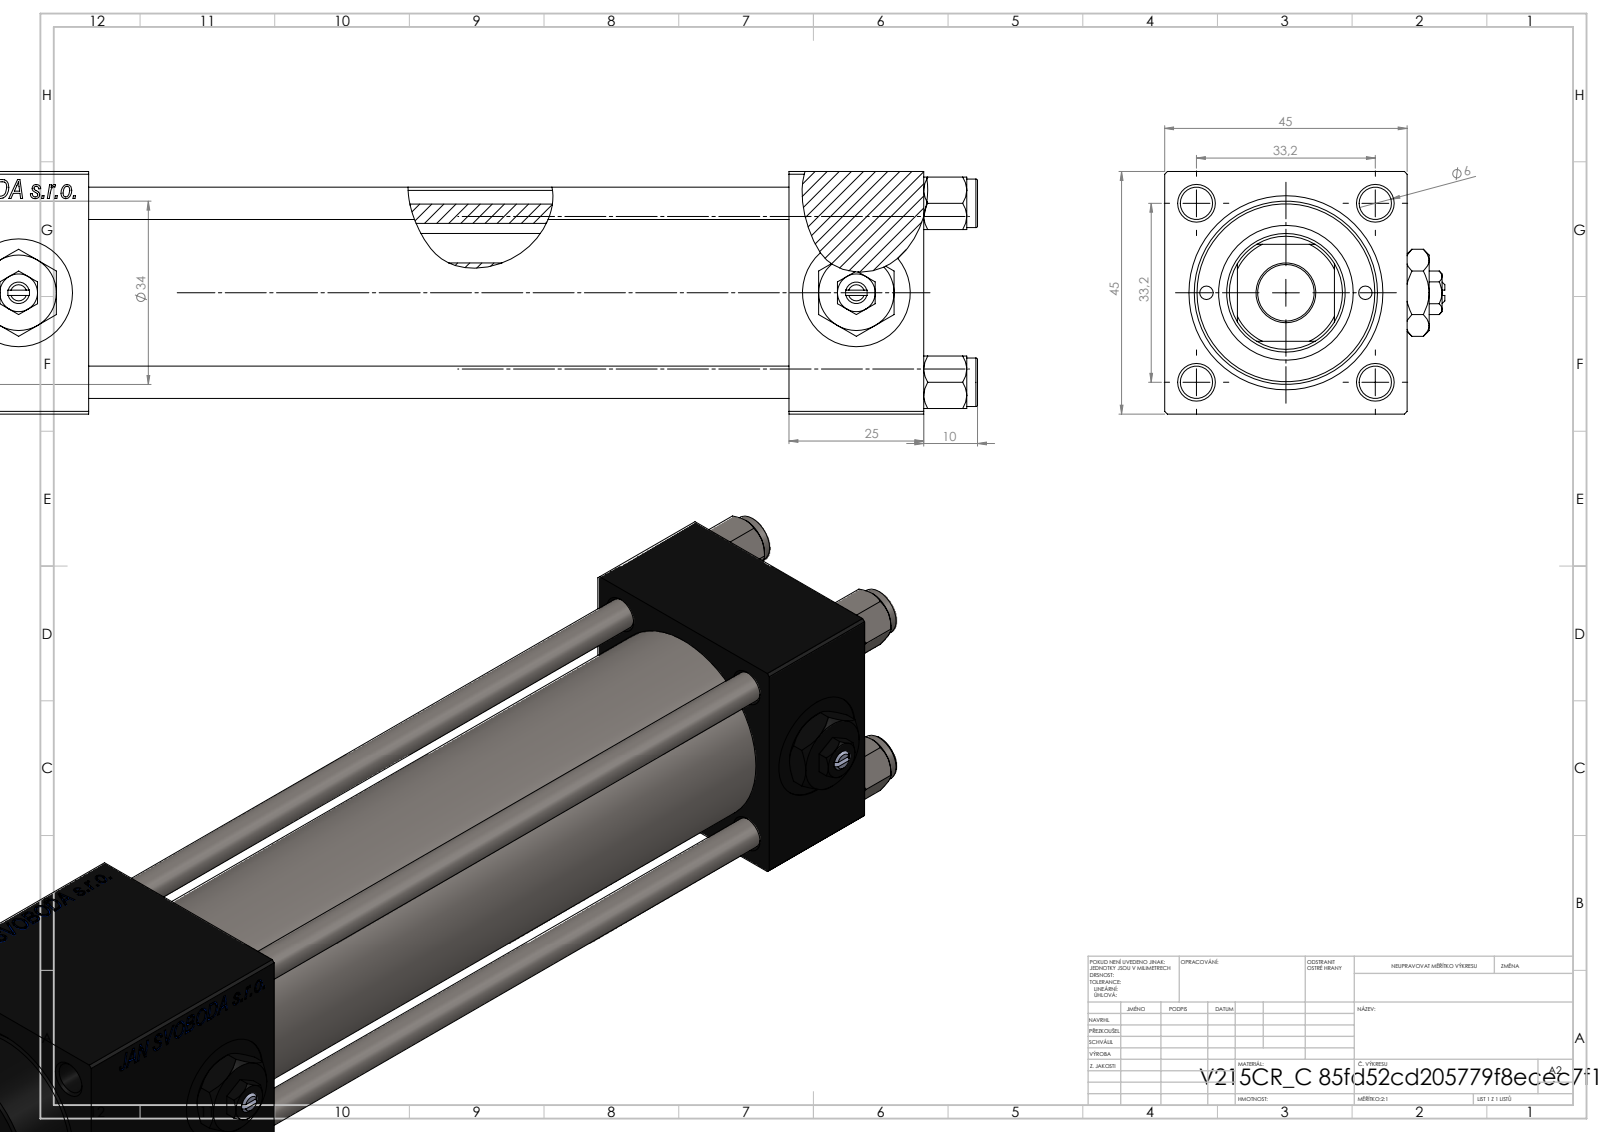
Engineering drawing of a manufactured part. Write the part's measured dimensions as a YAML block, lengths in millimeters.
part_name: "NUT_M5_C; V215CR_C_Body; V215CR_C_TYCINKA; V215CR_VCP_C (+2 more)"
step_written_by: "SolidWorks 2019 (CONFIG_CONTROL_DESIGN)"
units: millimeters
bodies: {solids: 13, faces: 1254, planar: 574, cylindrical: 102, other: 578}
overall_size: [238, 52, 45]
volume: 273986
surface_area: 102564
round_holes:
  - {diameter: 6, count: 4}
  - {diameter: 2.5, count: 2}
  - {diameter: 7, count: 2}
  - {diameter: 13.16, count: 2}
  - {diameter: 20, count: 2}
  - {diameter: 10.5, count: 1}
  - {diameter: 22, count: 1}
  - {diameter: 24, count: 1}
  - {diameter: 25, count: 1}
  - {diameter: 32, count: 1}
  - {diameter: 33, count: 1}
round_bosses_or_shafts:
  - {diameter: 9, count: 4}
  - {diameter: 38, count: 1}
  - {diameter: 34, count: 1}
partial_cylinders:
  - {radius: 10.5, count: 1}
face_to_face_distances: [45, 25, 203, 155, 130, 178, 44.8, 48, 174.3, 149.3]
hole_center_spacings: [16.7, 23.48, 33.2, 35.47, 14.75, 46.95, 29.5, 155.5]
